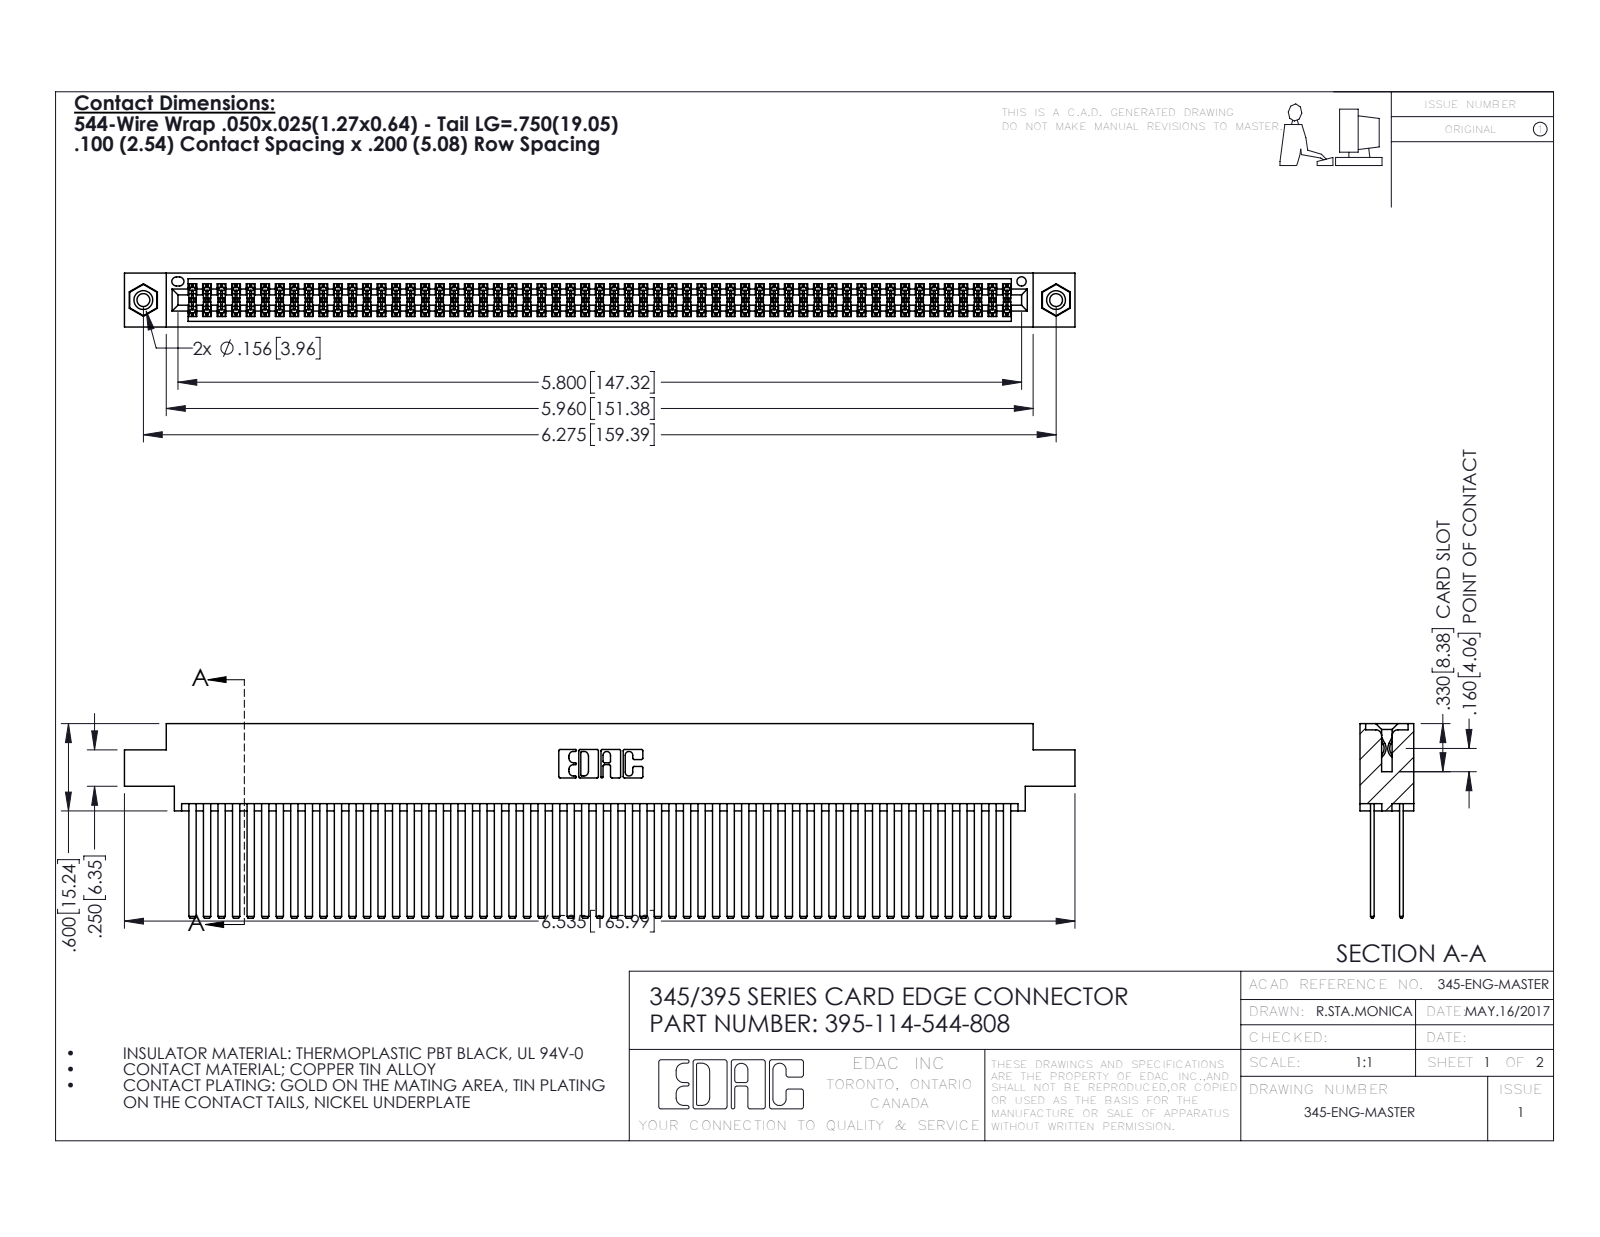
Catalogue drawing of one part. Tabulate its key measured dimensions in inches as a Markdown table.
| quantity | value |
| --- | --- |
| part name | 345 Part_0.170 Offset - 0.156 Dia-TI; 345-292-001_345-293-144; 345-250-001_345-250-003-102; 395-114-544-808 |
| STEP written by | SolidWorks 2016 (CONFIG_CONTROL_DESIGN) |
| units | inches |
| bodies | 117 solids, 5206 faces (3422 planar, 1768 cylindrical, 16 other) |
| overall size | 6.535 × 1.337 × 0.37 |
| volume | 1.083 in³ |
| surface area | 48.6 in² |
| round holes (diameter × count) | 0.089 × 2, 0.125 × 2, 0.156 × 2, 0.064 × 1 |
| round bosses / shafts (diameter × count) | 0.155 × 2 |
| partial cylindrical surfaces (radius × count) | 0.006 × 171, 0.01 × 22, 0.007 × 6, 0.031 × 6, 0.026 × 3, 0.014 × 2, 0.019 × 2, 0.022 × 2 |
| main face-to-face distances | 0.2, 0.025, 0.072, 0.098, 0.272, 0.298, 0.225, 0.175, 0.37, 0.15 |
| hole center spacings | 0.27, 6.039, 6.275 |
